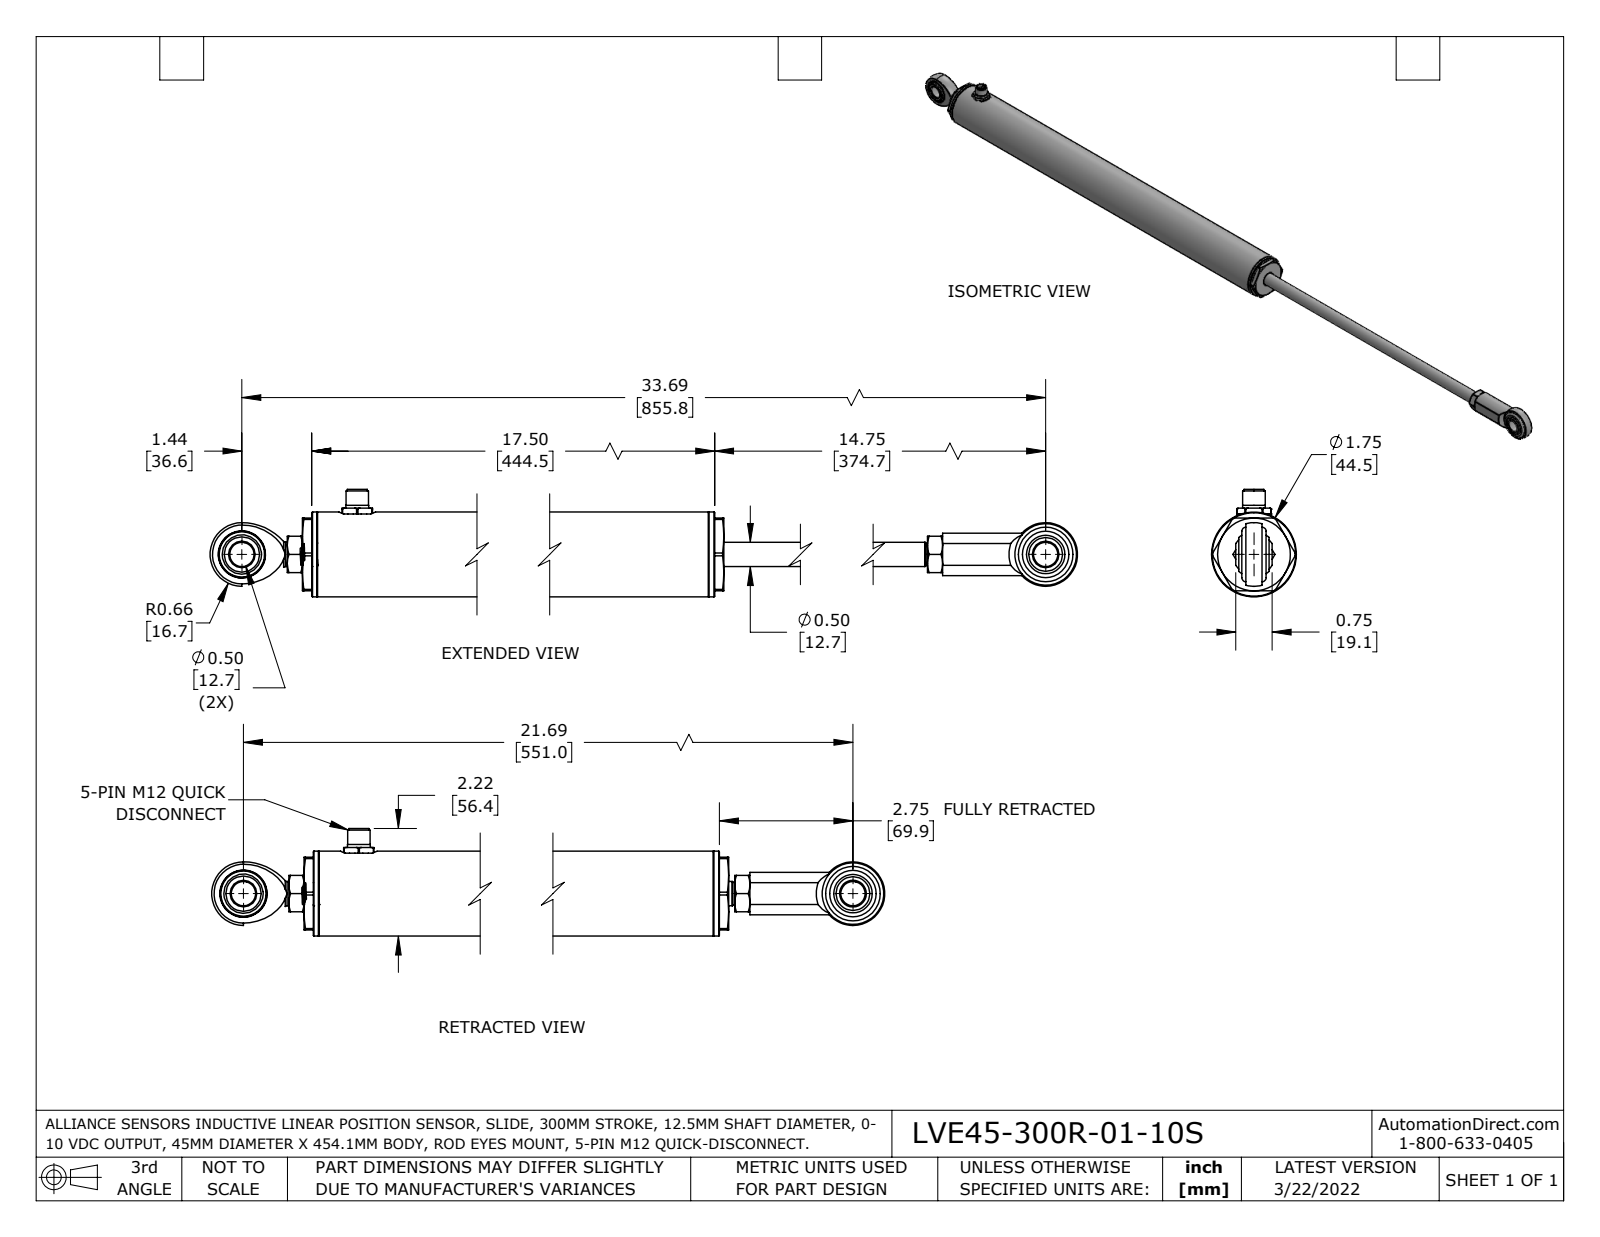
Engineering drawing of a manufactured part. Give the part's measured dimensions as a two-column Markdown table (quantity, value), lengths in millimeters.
| quantity | value |
| --- | --- |
| part name | 3100-0013; 3100-0027_98435A131; 3300-0003-XX_3300-0003-12; 3100-0023_9452K91 (+8 more) |
| STEP written by | SolidWorks 2021 (AUTOMOTIVE_DESIGN) |
| units | millimeters |
| bodies | 23 solids, 873 faces (198 planar, 297 cylindrical, 378 other) |
| overall size | 889.1 × 56.4 × 44.5 |
| volume | 336 300 mm³ |
| surface area | 200 600 mm² |
| round holes (diameter × count) | 12.7 × 3, 5 × 1, 6.4 × 1, 6.7 × 1, 7.8 × 1, 8.4 × 1, 8.6 × 1, 10.5 × 1, 10.6 × 1, 11.5 × 1, 12.1 × 1, 12.7 × 1 |
| round bosses / shafts (diameter × count) | 0.8 × 5, 44.5 × 1, 41.3 × 1, 39.7 × 1, 38.9 × 1, 38.1 × 1, 37.3 × 1, 35.2 × 1 |
| partial cylindrical surfaces (radius × count) | 8.3 × 1, 9 × 1, 9.6 × 1, 9.7 × 1, 11.1 × 1, 21.6 × 1 |
| main face-to-face distances | 49, 12.7, 9.7, 17.5, 66.5, 395.6, 56.9, 39.4, 400.4, 382.9 |
| hole center spacings | 12.7, 855.8 |
